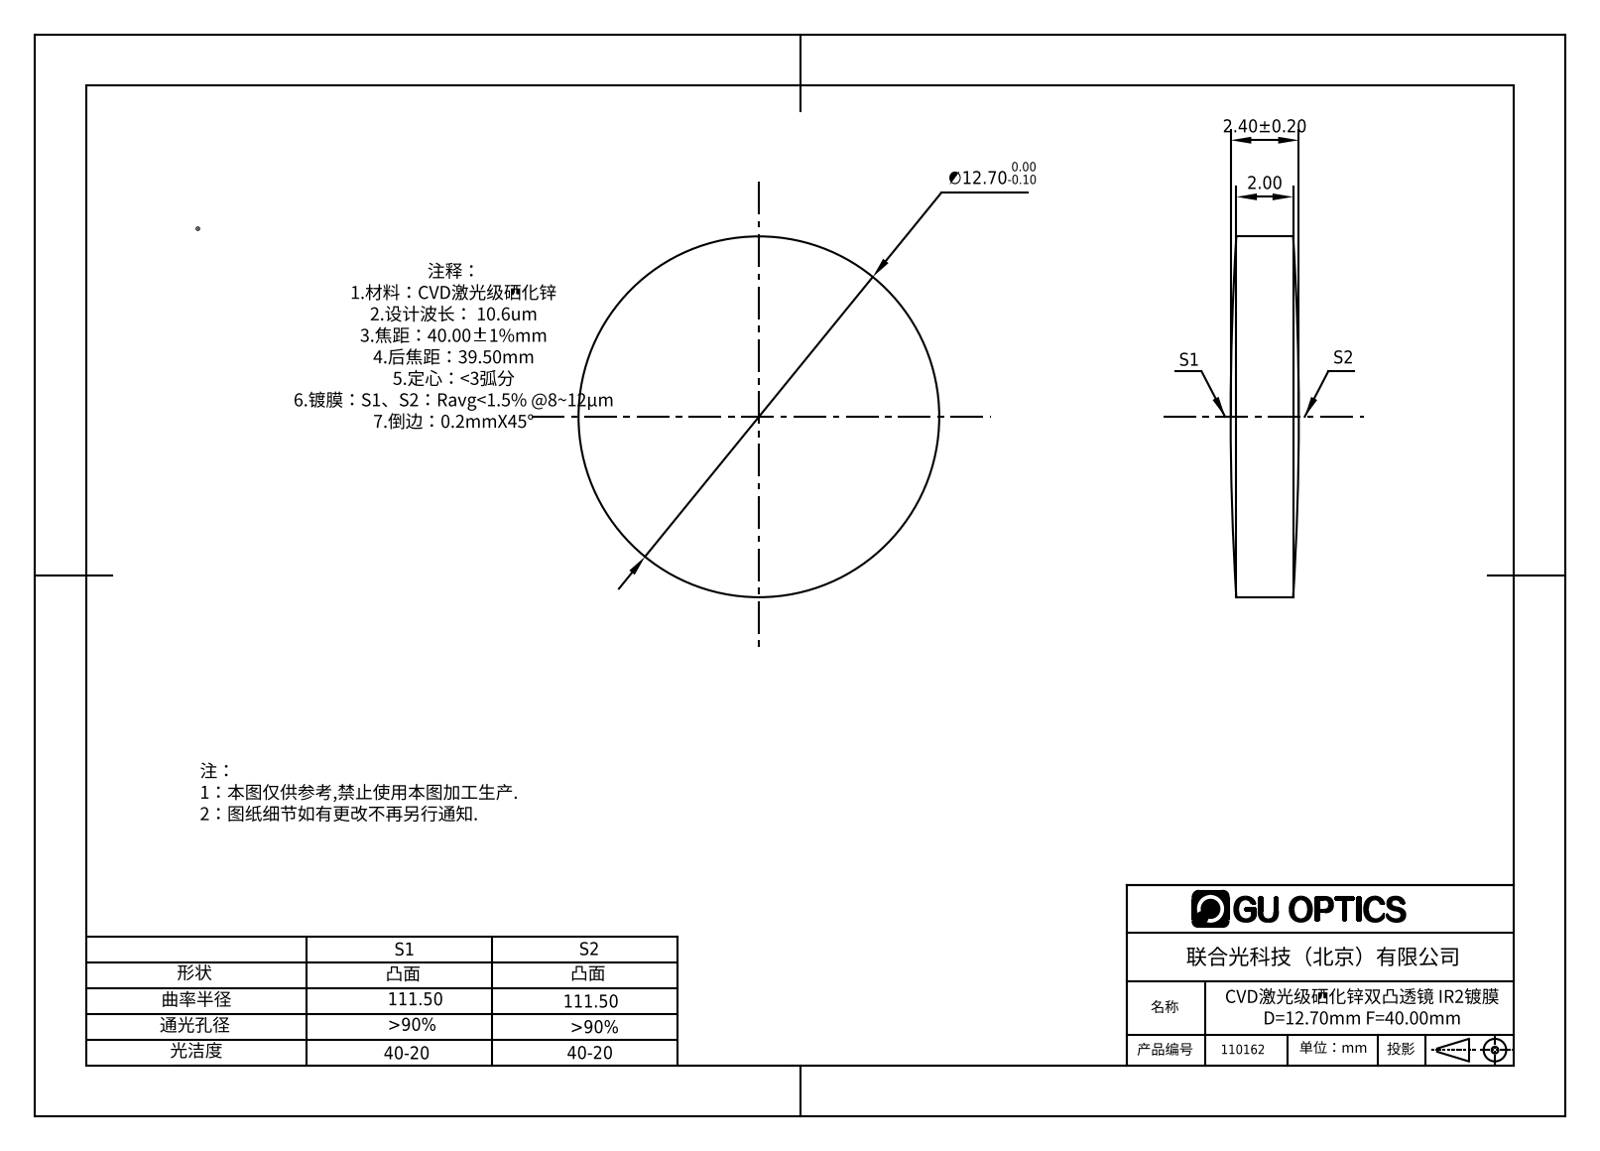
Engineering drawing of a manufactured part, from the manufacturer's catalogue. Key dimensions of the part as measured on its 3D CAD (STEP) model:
Part name (STEP PRODUCT): 110154
STEP written by: SolidWorks 2016 (CONFIG_CONTROL_DESIGN)
Units: millimetres
Bodies: 1 solid, 6 faces (0 planar, 2 cylindrical, 4 other)
Overall size (bounding box): 12.7 × 12.7 × 2.4
Volume: 279 mm³ · Surface area: 333 mm²
Round bosses / shafts (diameter × count): ⌀12.7 ×1
